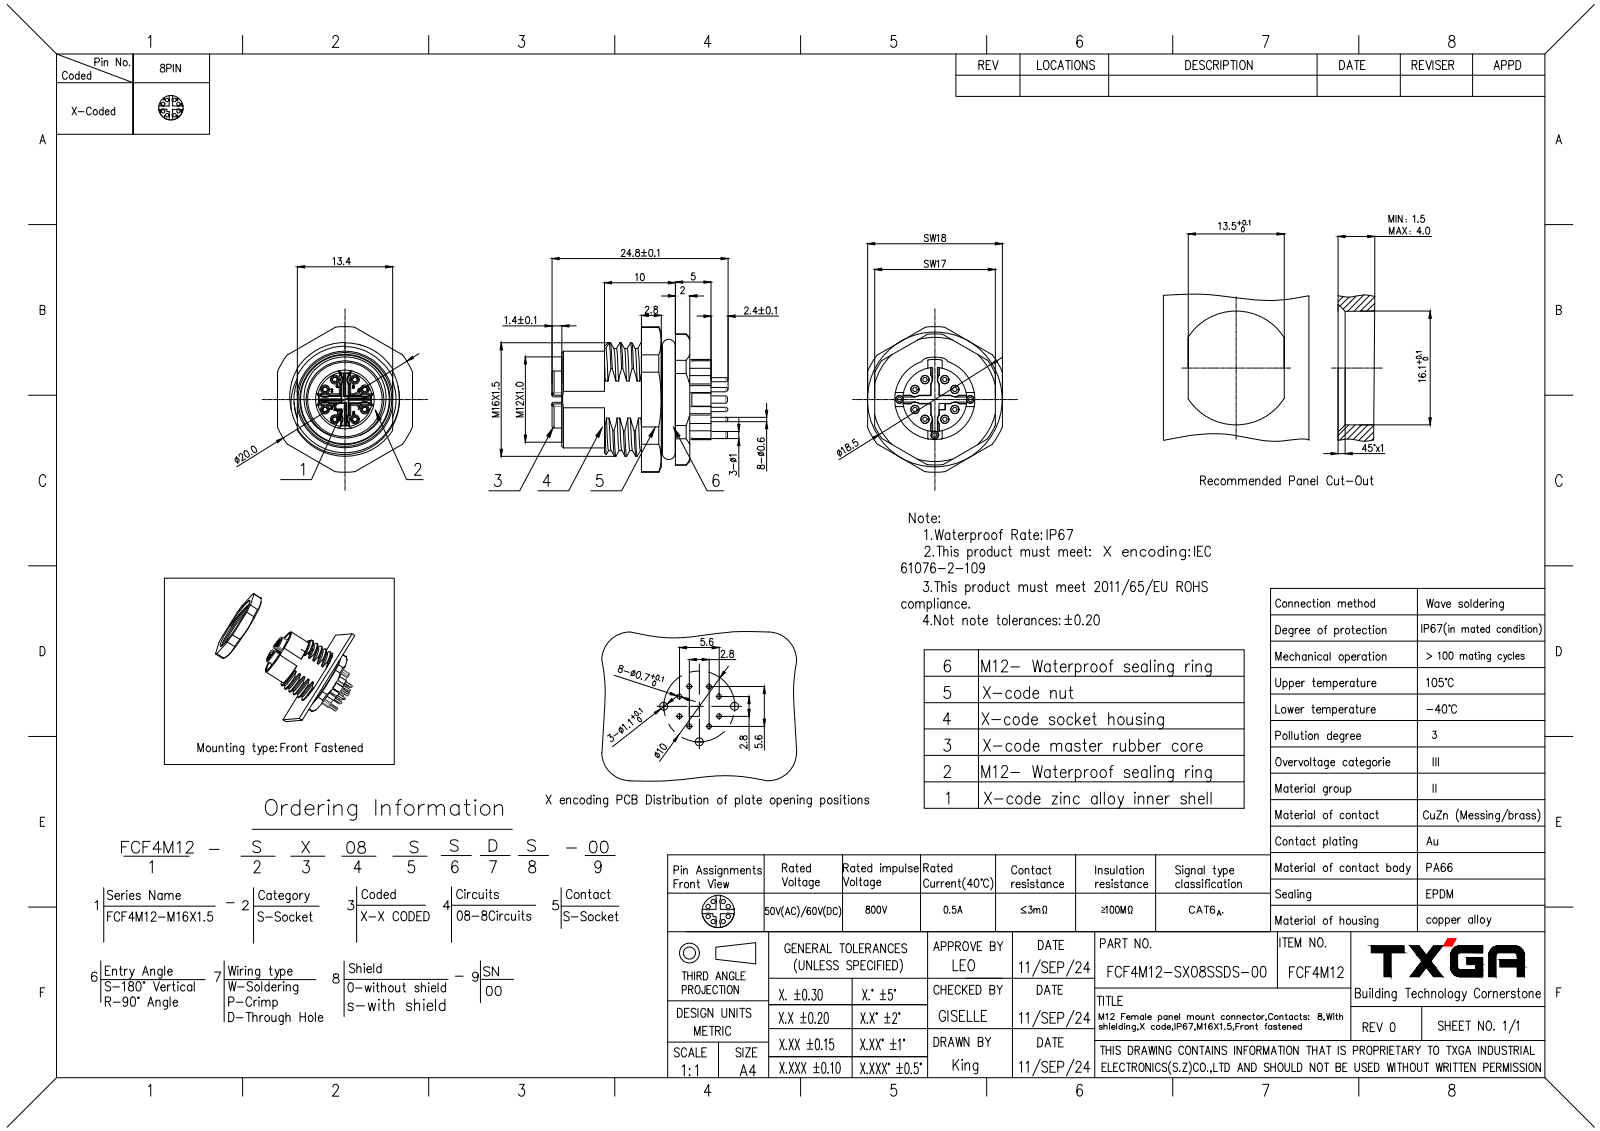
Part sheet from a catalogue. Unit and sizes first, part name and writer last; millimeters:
Units: millimetres
Overall size (bounding box): 24.79 × 20.5 × 19
Round holes (diameter × count): ⌀0.65 ×8, ⌀0.7 ×8, ⌀1.2 ×8, ⌀1.25 ×8, ⌀10.92 ×1, ⌀12.2 ×1, ⌀12.5 ×1
Round bosses / shafts (diameter × count): ⌀1.15 ×8, ⌀0.6 ×8, ⌀1 ×3, ⌀13.6 ×1, ⌀13.3 ×1, ⌀8.25 ×1
Partial cylindrical surfaces — rounded edges, fillets, slot ends (radius × count): R0.1 ×56, R0.3 ×8, R1 ×8, R1.05 ×8, R0.2 ×4, R3.65 ×1, R3.75 ×1, R4.5 ×1
Main face-to-face distances: 2.8, 8.41, 1, 2, 18, 5.61, 1.15, 6.1, 1.1, 13.4
Hole centre spacings: 3.13, 4.43, 1.98, 2.8, 5.6, 5.94, 6.26
Volume: 3 054 mm³ · Surface area: 4 172 mm²
Bodies: 1 solid, 974 faces (341 planar, 341 cylindrical, 292 other)
Part name (STEP PRODUCT): F04M12-SX08SSD0-00
STEP written by: SolidWorks 2021 (CONFIG_CONTROL_DESIGN)
